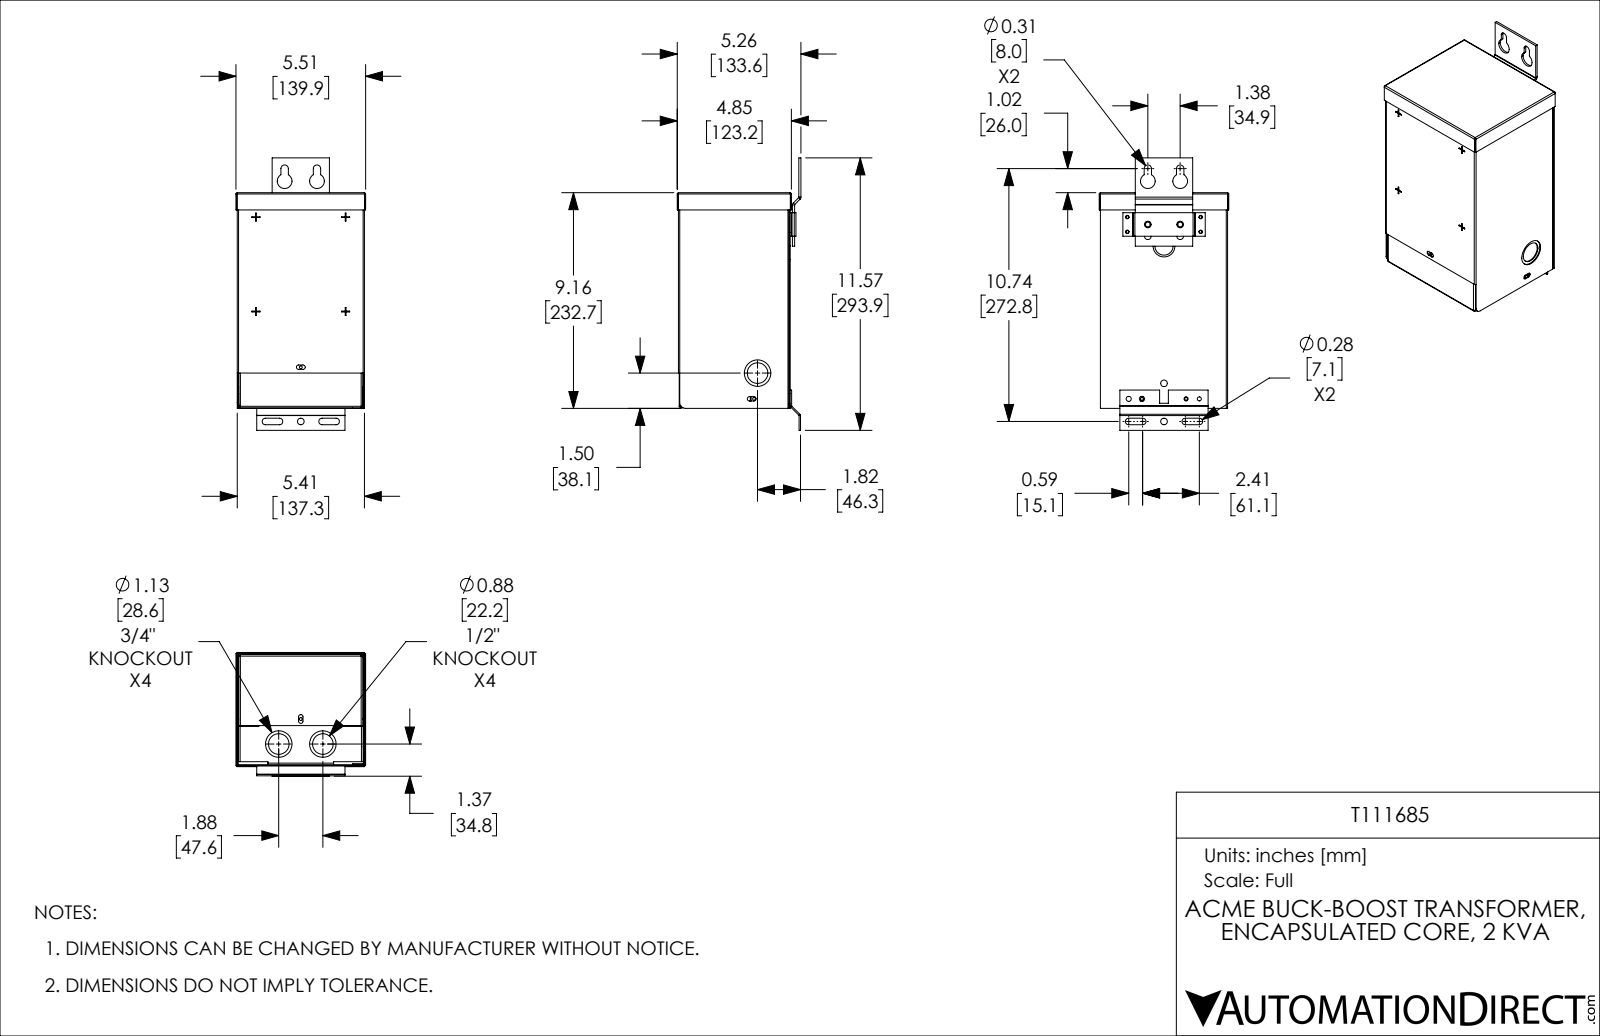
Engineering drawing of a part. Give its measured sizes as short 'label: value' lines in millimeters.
name: T111685
written by: SolidWorks 2021 (CONFIG_CONTROL_DESIGN)
unit: mm
bodies: 7 solids, 521 faces (329 planar, 152 cylindrical, 40 other)
size: 293.87 × 139.9 × 133.57
volume: 177 414 mm³; area: 368 059 mm²
holes: 6× ⌀7.14, 5× ⌀3.05, 3× ⌀22.22, 3× ⌀28.57, 2× ⌀4.37, 2× ⌀4.76, 2× ⌀5.11, 2× ⌀5.56, 2× ⌀15.88
bosses: 1× ⌀29.79, 1× ⌀23.44
rounds: 10× R0.51, 10× R2.38, 8× R0.79, 8× R1.42, 8× R1.7, 4× R0.38, 4× R1.9, 4× R3.57
face distances: 0.91, 119.74, 136.41, 118.83, 135.5, 137.32, 120.65, 231.14, 1.29, 2.2
hole spacings: 34.92, 12.7, 14.29, 29.09, 34.08, 35.98, 37.16, 41.6
